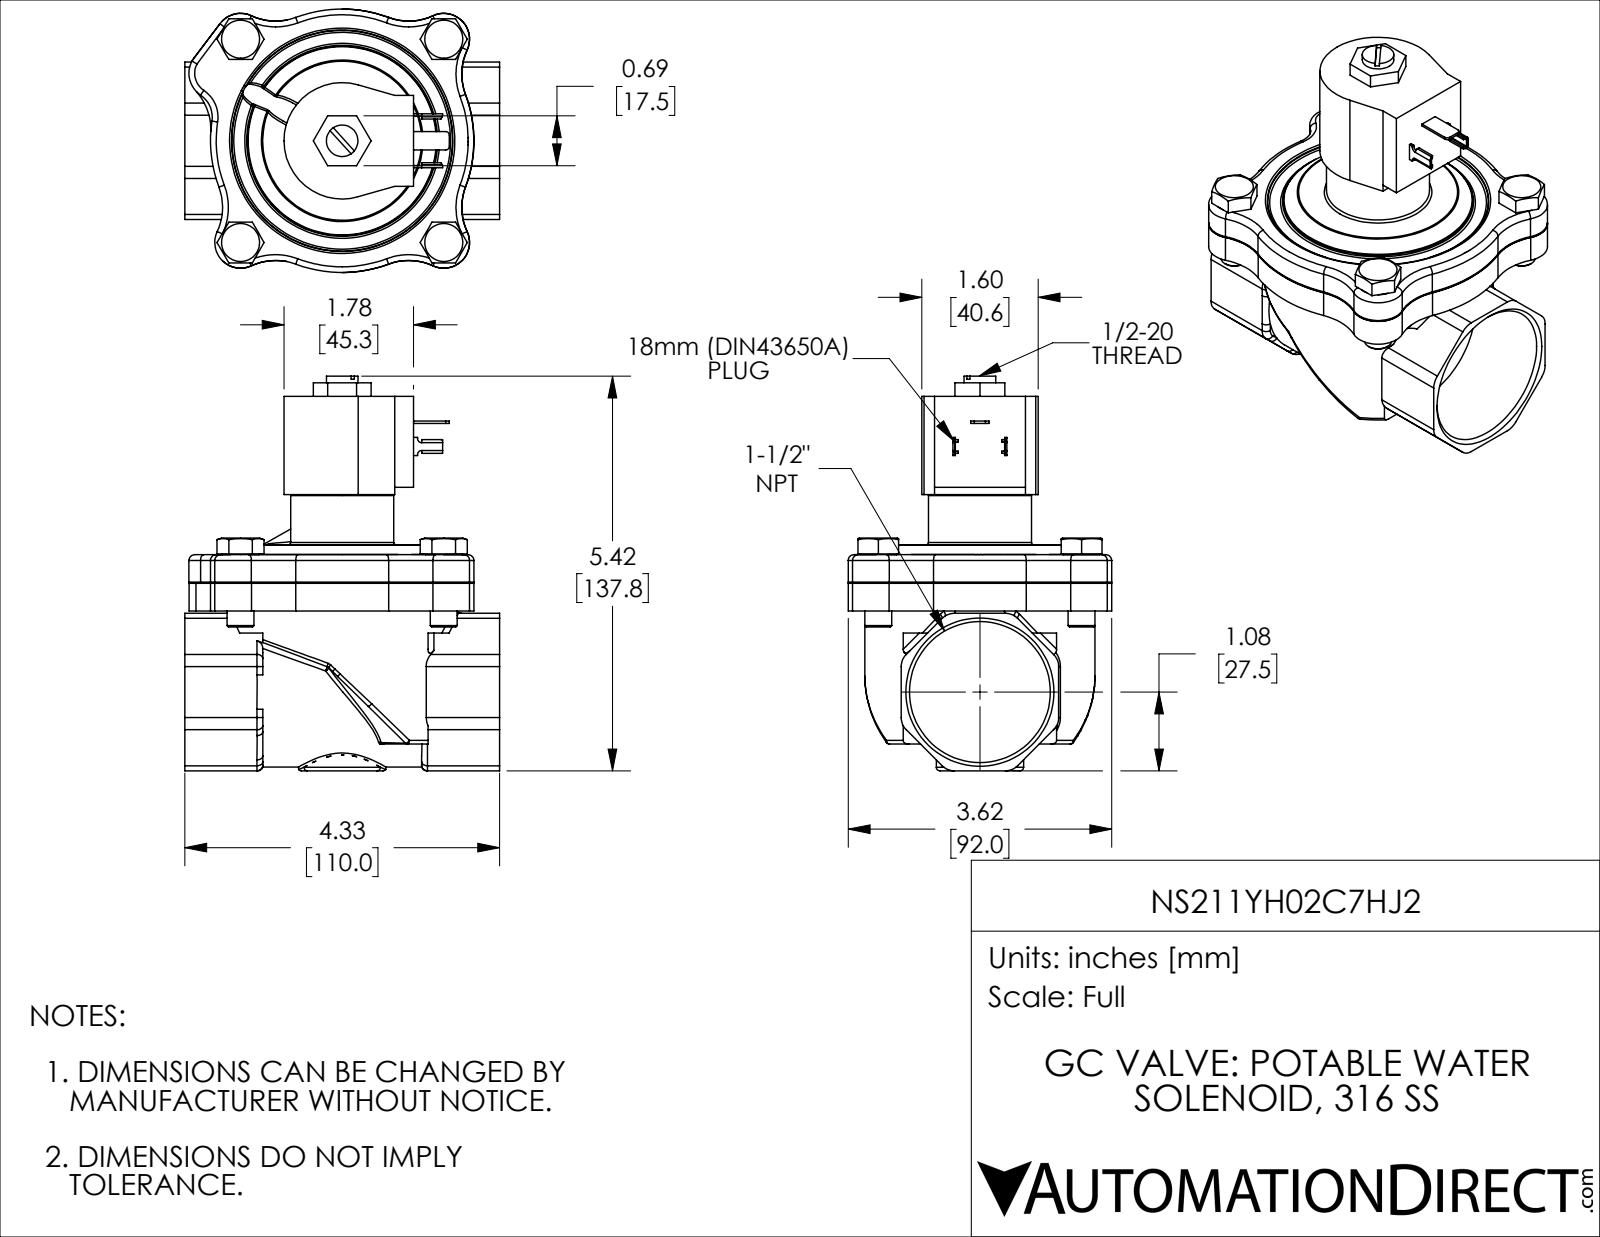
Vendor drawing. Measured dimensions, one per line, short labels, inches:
name: NS211YH02C7HJ2
written by: SolidWorks 2024 (CONFIG_CONTROL_DESIGN)
unit: in
bodies: 9 solids, 520 faces (159 planar, 158 cylindrical, 203 other)
size: 5.424 × 4.33 × 3.622
volume: 25.63 in³; area: 136.4 in²
holes: 4× ⌀0.375, 4× ⌀0.433, 1× ⌀0.125, 1× ⌀0.434, 1× ⌀0.846, 1× ⌀0.949, 1× ⌀1.937
bosses: 4× ⌀0.504, 4× ⌀0.37, 1× ⌀3.165, 1× ⌀1.417, 1× ⌀1.2
rounds: 15× R0.787, 13× R0.08, 8× R0.236, 8× R0.354, 4× R0.006, 4× R0.041, 2× R0.05, 2× R0.06
face distances: 0.382, 0.775, 0.393, 1.83, 1.602, 1.22, 0.827, 2.952, 2.57, 2.177
hole spacings: 2.795, 1.976, 1.977, 2.794, 2.795, 3.952, 3.953
